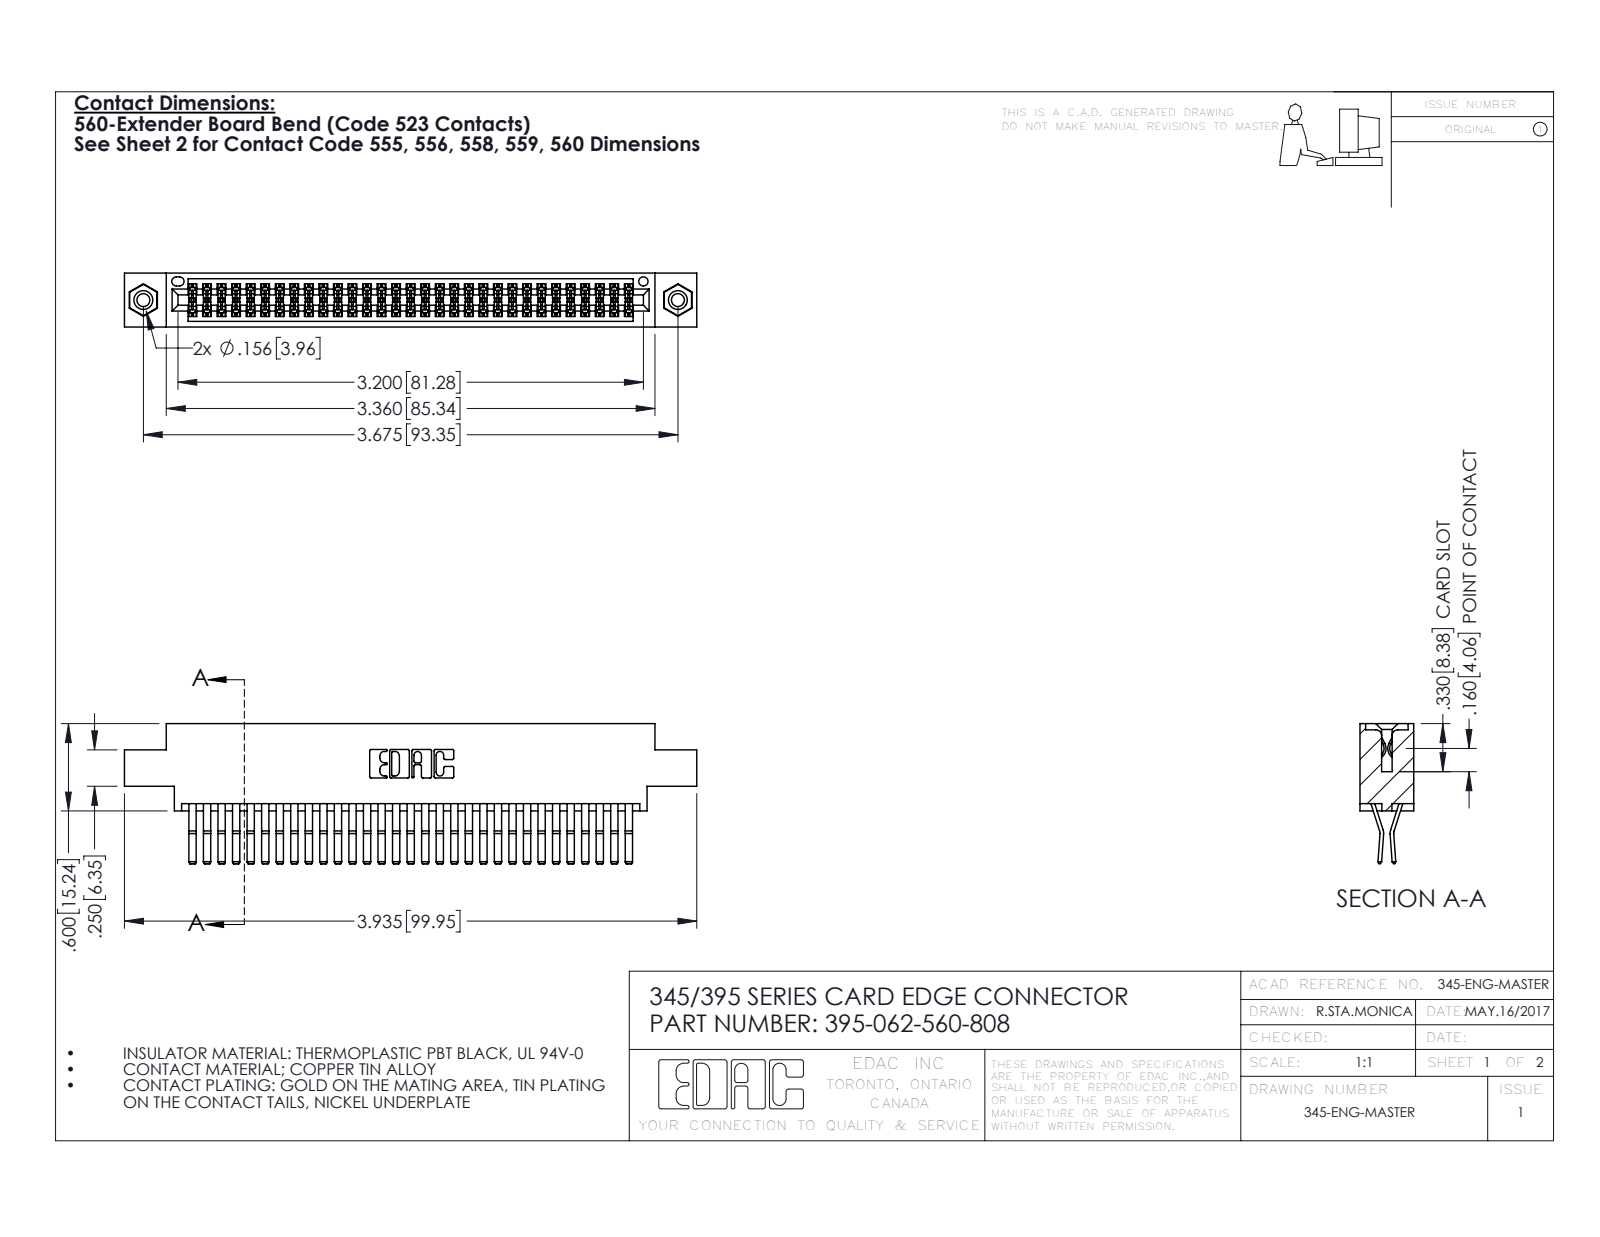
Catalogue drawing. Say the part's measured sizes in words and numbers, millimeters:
The part is named "345-250-001_345-250-003-102; 395-062-560-808; 345 Part_0.170 Offset - 0.156 Dia-TI; 345-292-001_560 Tail". Its 3-D file was written by "SolidWorks 2016 (CONFIG_CONTROL_DESIGN)". It is 65 solids with 3414 faces: 2162 planar, 1236 cylindrical and 16 other. Overall it measures 99.9 by 24.4 by 9.4 millimeters. Its volume is 9 900 cubic millimeters and its surface area 15 610 square millimeters. Round holes: 2 of diameter 2.3, 2 of diameter 3.2, 2 of diameter 4, 1 of diameter 1.6. Round bosses or shafts: 2 of diameter 3.9. Partial cylindrical surfaces (rounded edges, fillets, slot ends): 94 of radius 0.2, 22 of radius 0.3, 6 of radius 0.2, 6 of radius 0.8, 3 of radius 0.7, 2 of radius 0.3, 2 of radius 0.4, 2 of radius 0.5. The main face-to-face distances are 0.6, 1.8, 7.6, 9.4, 5.1, 2.5, 6.9, 5.7, 4.4, 3.8. The hole center spacings are 6.9, 87.4, 93.3.
